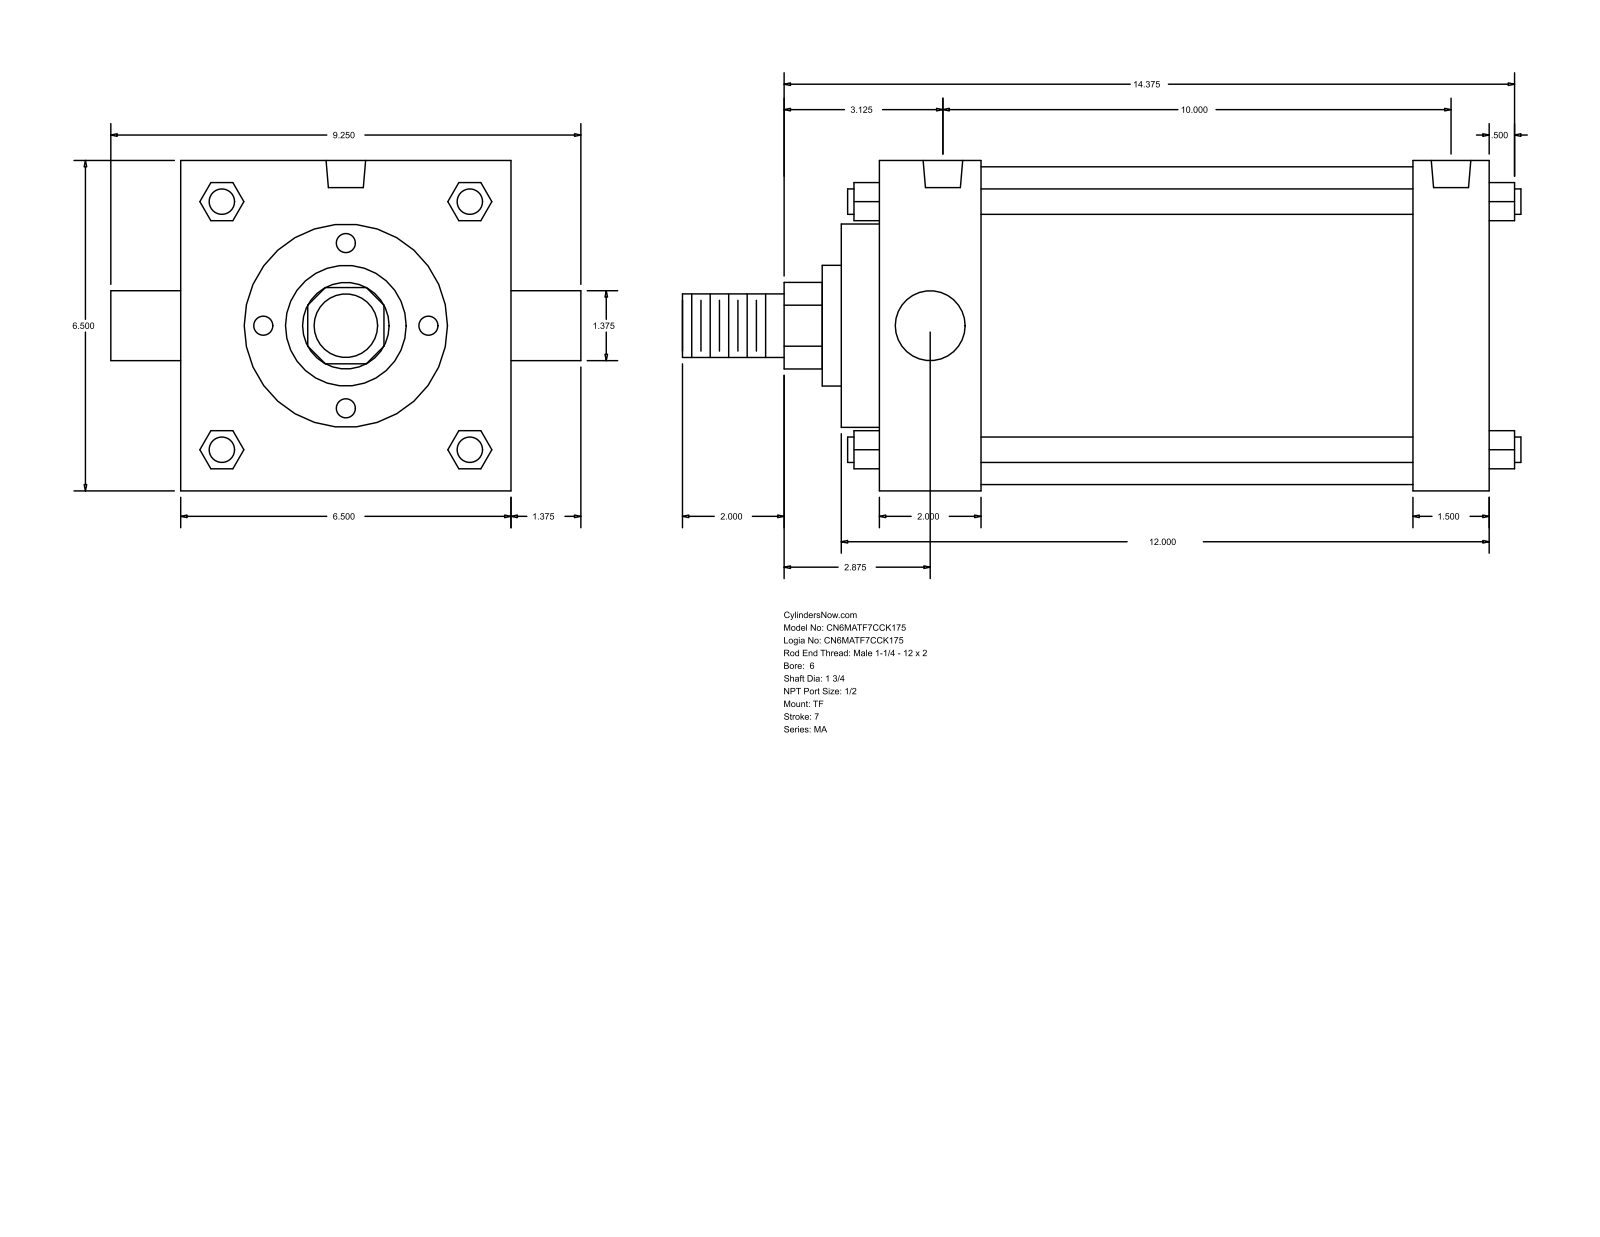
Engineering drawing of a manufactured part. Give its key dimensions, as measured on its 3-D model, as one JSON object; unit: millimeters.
{"part_name": "MA_TF__0600_1.75", "step_written_by": "GSSL Pune (CONFIG_CONTROL_DESIGN)", "units": "millimeters", "bodies": {"solids": 0, "faces": 122, "planar": 93, "cylindrical": 29, "other": 0}, "overall_size": [419.1, 234.95, 165.1], "round_holes": [[17.46, 3], [19.77, 2]], "round_bosses_or_shafts": [[12.7, 4], [158.75, 1], [101.6, 1], [60.33, 1], [44.45, 1], [34.92, 1], [31.75, 1]], "partial_cylinders_radius": [[21.63, 1]], "face_to_face_distances": [165.1, 304.81, 19.05, 50.8, 266.7, 254.01, 215.9, 38.11, 69.85, 285.75], "hole_center_spacings": [254]}
